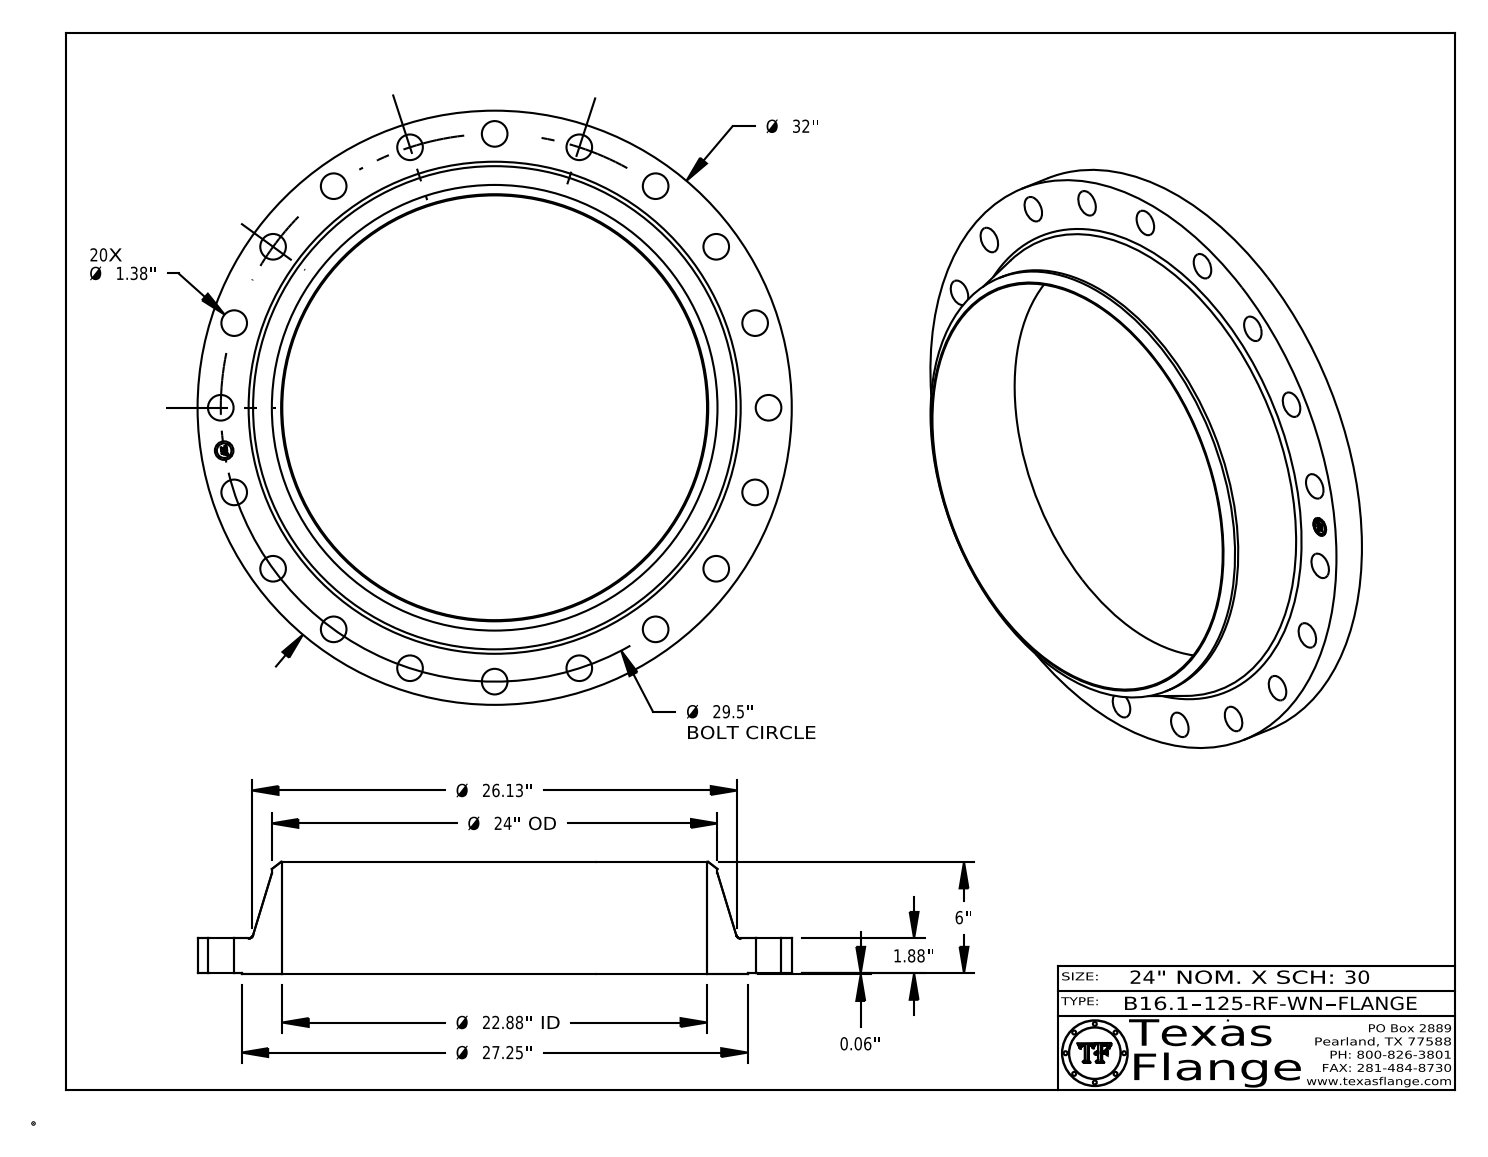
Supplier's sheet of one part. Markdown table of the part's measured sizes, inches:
| quantity | value |
| --- | --- |
| part name | B16.1, Class 125-RF-WN |
| STEP written by | CATIA V5 STEP AP214 (AUTOMOTIVE_DESIGN) |
| units | inches |
| bodies | 1 solid, 443 faces (369 planar, 68 cylindrical, 6 other) |
| overall size | 32 × 32 × 6.063 |
| volume | 1 003 in³ |
| surface area | 1 747 in² |
| round holes (diameter × count) | 1.38 × 20, 1 × 1, 22.876 × 1 |
| round bosses / shafts (diameter × count) | 0.061 × 8, 32 × 1, 27.25 × 1, 24 × 1, 0.788 × 1 |
| main face-to-face distances | 1.88, 0.063, 1.943, 6.063, 6, 4.12, 1.928, 1.865, 0.015, 4.135 |
| hole center spacings | 14.75, 29.137, 4.615, 17.34, 20.859, 23.866, 26.285, 9.116 |
